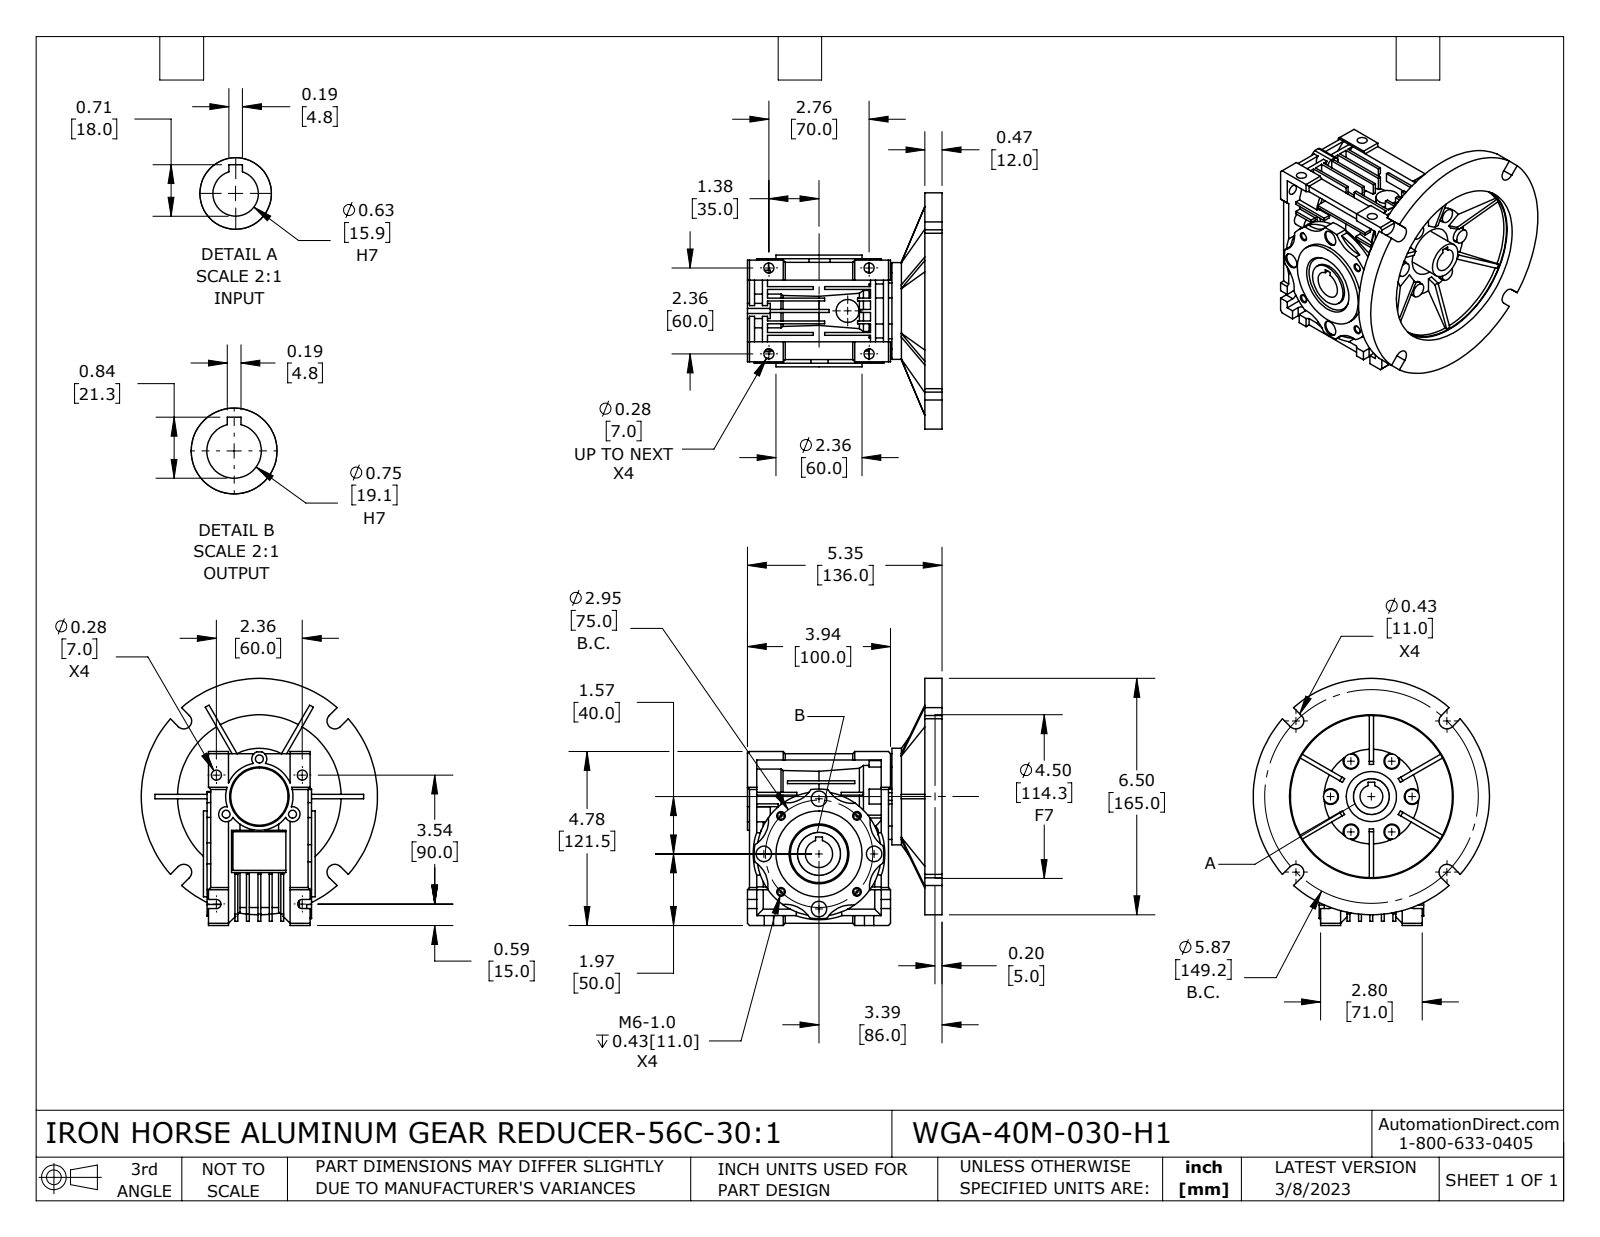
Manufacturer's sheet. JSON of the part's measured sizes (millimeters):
{"part_name": "WGA-40M-030-H1", "step_written_by": "SolidWorks 2021 (CONFIG_CONTROL_DESIGN)", "units": "millimeters", "bodies": {"solids": 4, "faces": 856, "planar": 511, "cylindrical": 251, "other": 94}, "overall_size": [172.5, 165, 136], "volume_mm3": 824900, "surface_area_mm2": 203200, "round_holes": [[7, 6], [11, 6], [4.9, 4], [10.8, 4], [5.6, 3], [15.9, 1], [16.5, 1], [19.1, 1], [23, 1], [28, 1], [30, 1], [35, 1]], "round_bosses_or_shafts": [[10, 6], [165, 1], [75, 1], [67.5, 1], [60, 1], [54, 1], [47, 1], [36, 1]], "partial_cylinders_radius": [[20, 8], [3.2, 6], [5.2, 6], [5.5, 4], [5.3, 3], [43.5, 1], [43.6, 1], [45.2, 1]], "face_to_face_distances": [8, 12, 2, 24, 6, 1.5, 16, 2.5, 10, 5], "hole_center_spacings": [28.5, 29.1, 70.2, 49.4, 37.5, 38.5, 53, 54.5]}
